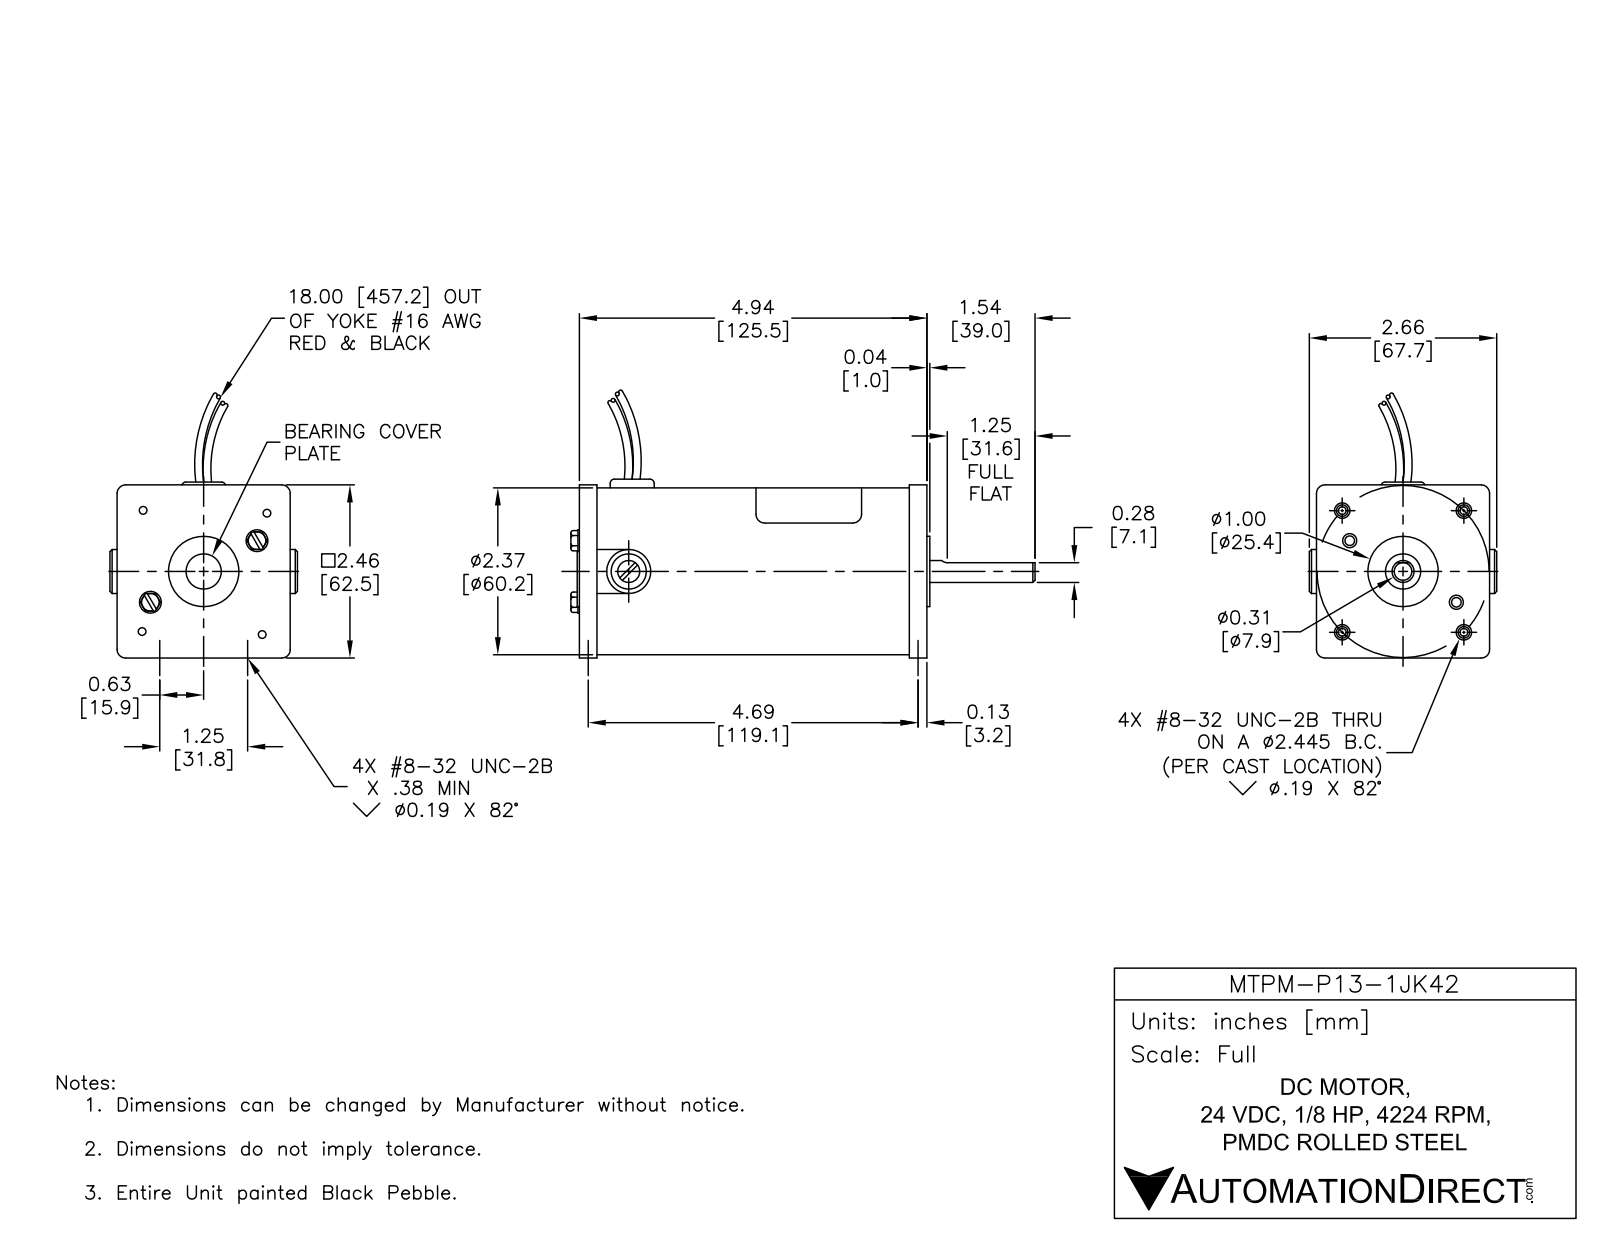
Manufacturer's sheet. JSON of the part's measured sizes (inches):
{"part_name": "MTPM-P13-1JK42", "step_written_by": "SolidWorks 2013 (AUTOMOTIVE_DESIGN)", "units": "inches", "bodies": {"solids": 20, "faces": 150, "planar": 71, "cylindrical": 76, "other": 3}, "overall_size": [6.604, 3.71, 2.602], "volume_in3": 5.787, "surface_area_in2": 111.7, "round_holes": [[0.063, 4], [0.156, 2], [0.25, 1], [0.562, 1], [1, 1], [2.25, 1]], "round_bosses_or_shafts": [[0.312, 4], [0.1, 2], [2.375, 1], [0.625, 1], [0.625, 1]], "face_to_face_distances": [0.25, 4.694, 4.444, 4.944, 2.46, 4.981, 4.731, 0.287, 0.037, 0.25], "hole_center_spacings": [1.223, 1.729, 0.44, 0.875, 1.306, 1.678, 2.08, 2.445]}
